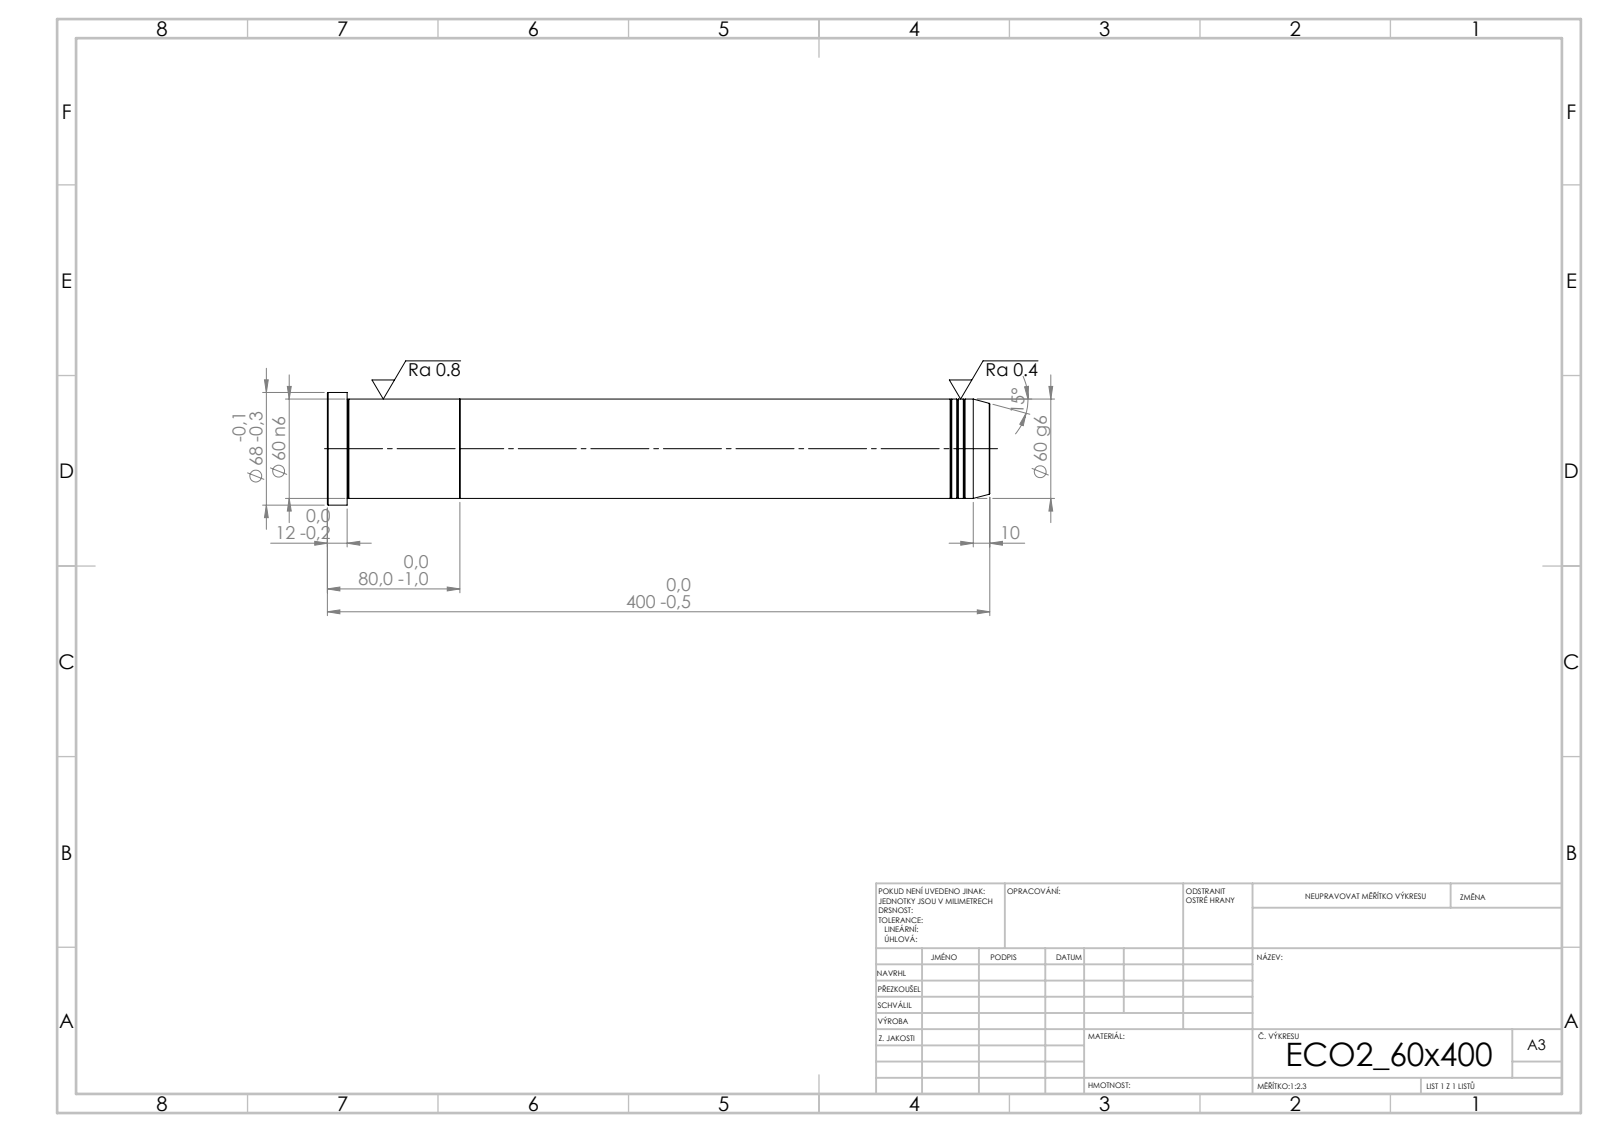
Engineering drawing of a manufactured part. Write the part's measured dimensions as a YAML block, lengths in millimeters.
step_written_by: "SolidWorks 2019 (CONFIG_CONTROL_DESIGN)"
units: millimeters
bodies: {solids: 2, faces: 39, planar: 5, cylindrical: 12, other: 22}
overall_size: [400, 68, 68]
volume: 1138000
surface_area: 88450
round_bosses_or_shafts:
  - {diameter: 68, count: 1}
  - {diameter: 60, count: 1}
face_to_face_distances: [80, 320, 400, 388, 68, 12]
